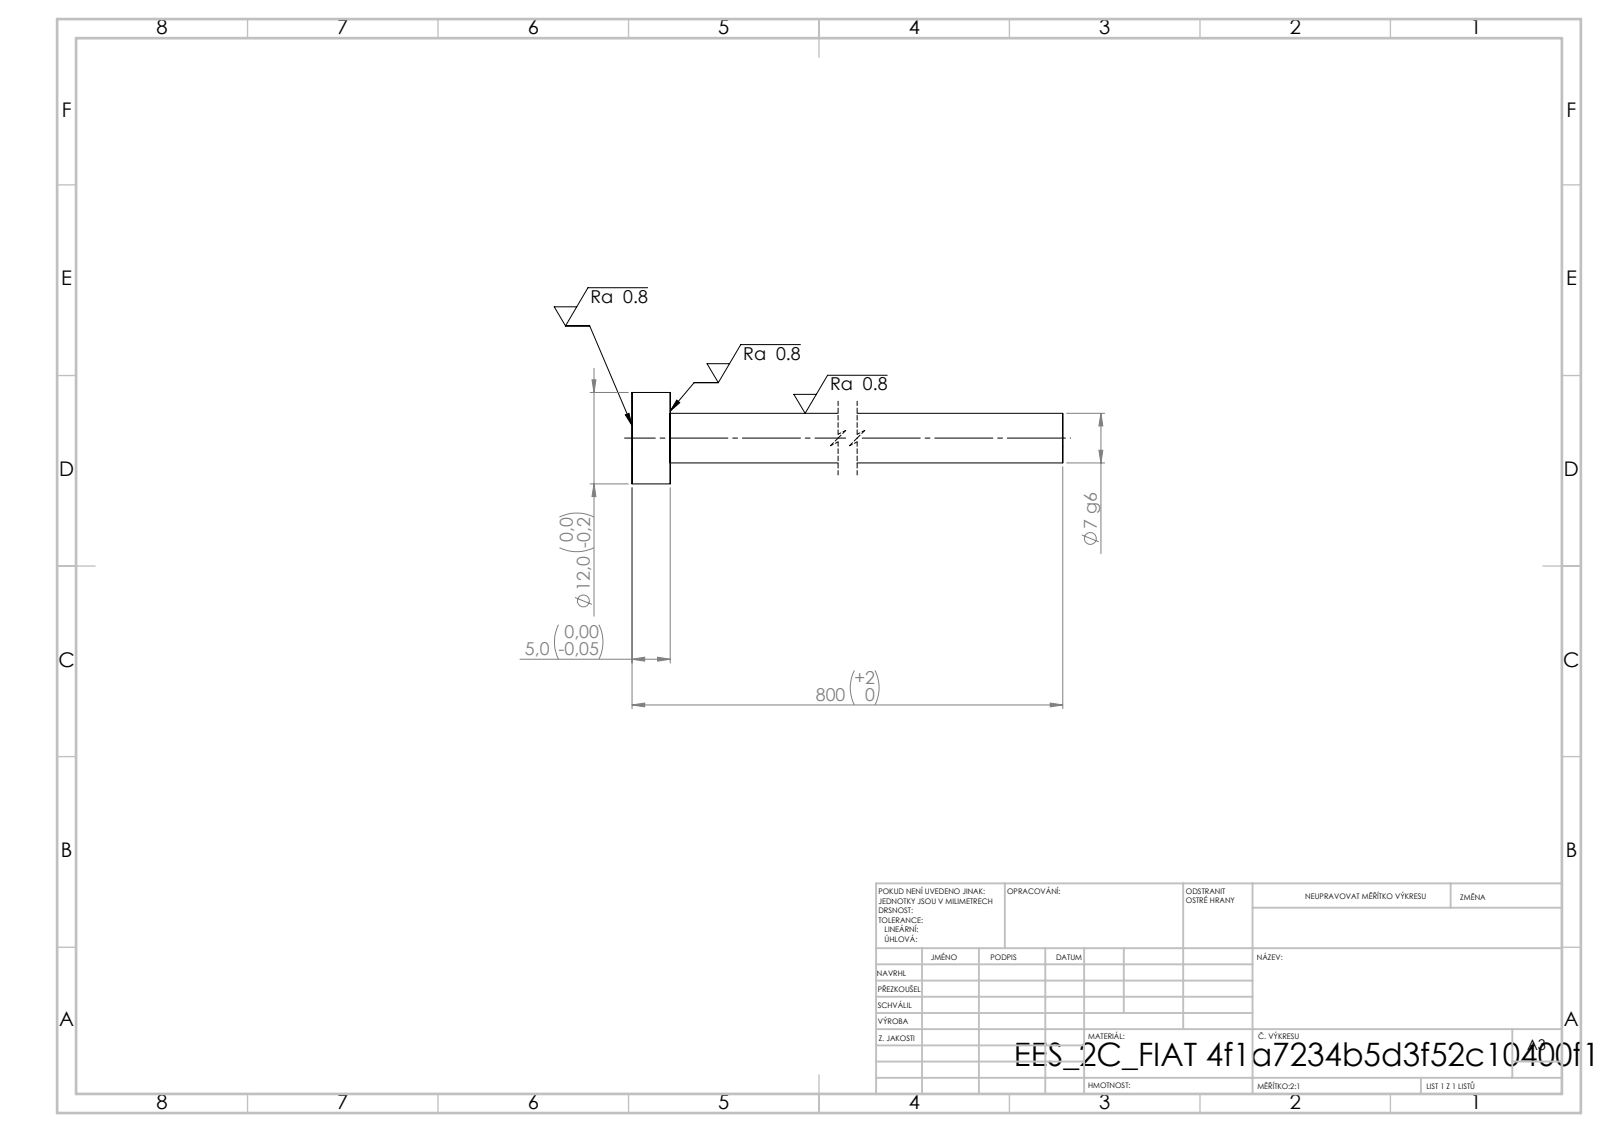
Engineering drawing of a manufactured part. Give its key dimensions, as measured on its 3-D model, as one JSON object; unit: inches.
{"step_written_by": "SolidWorks 2019 (CONFIG_CONTROL_DESIGN)", "units": "inches", "bodies": {"solids": 1, "faces": 7, "planar": 3, "cylindrical": 4, "other": 0}, "overall_size": [31.496, 0.472, 0.472], "volume_in3": 1.644, "surface_area_in2": 25.81, "round_bosses_or_shafts": [[0.472, 1], [0.256, 1]], "face_to_face_distances": [0.197, 31.496, 31.299]}
